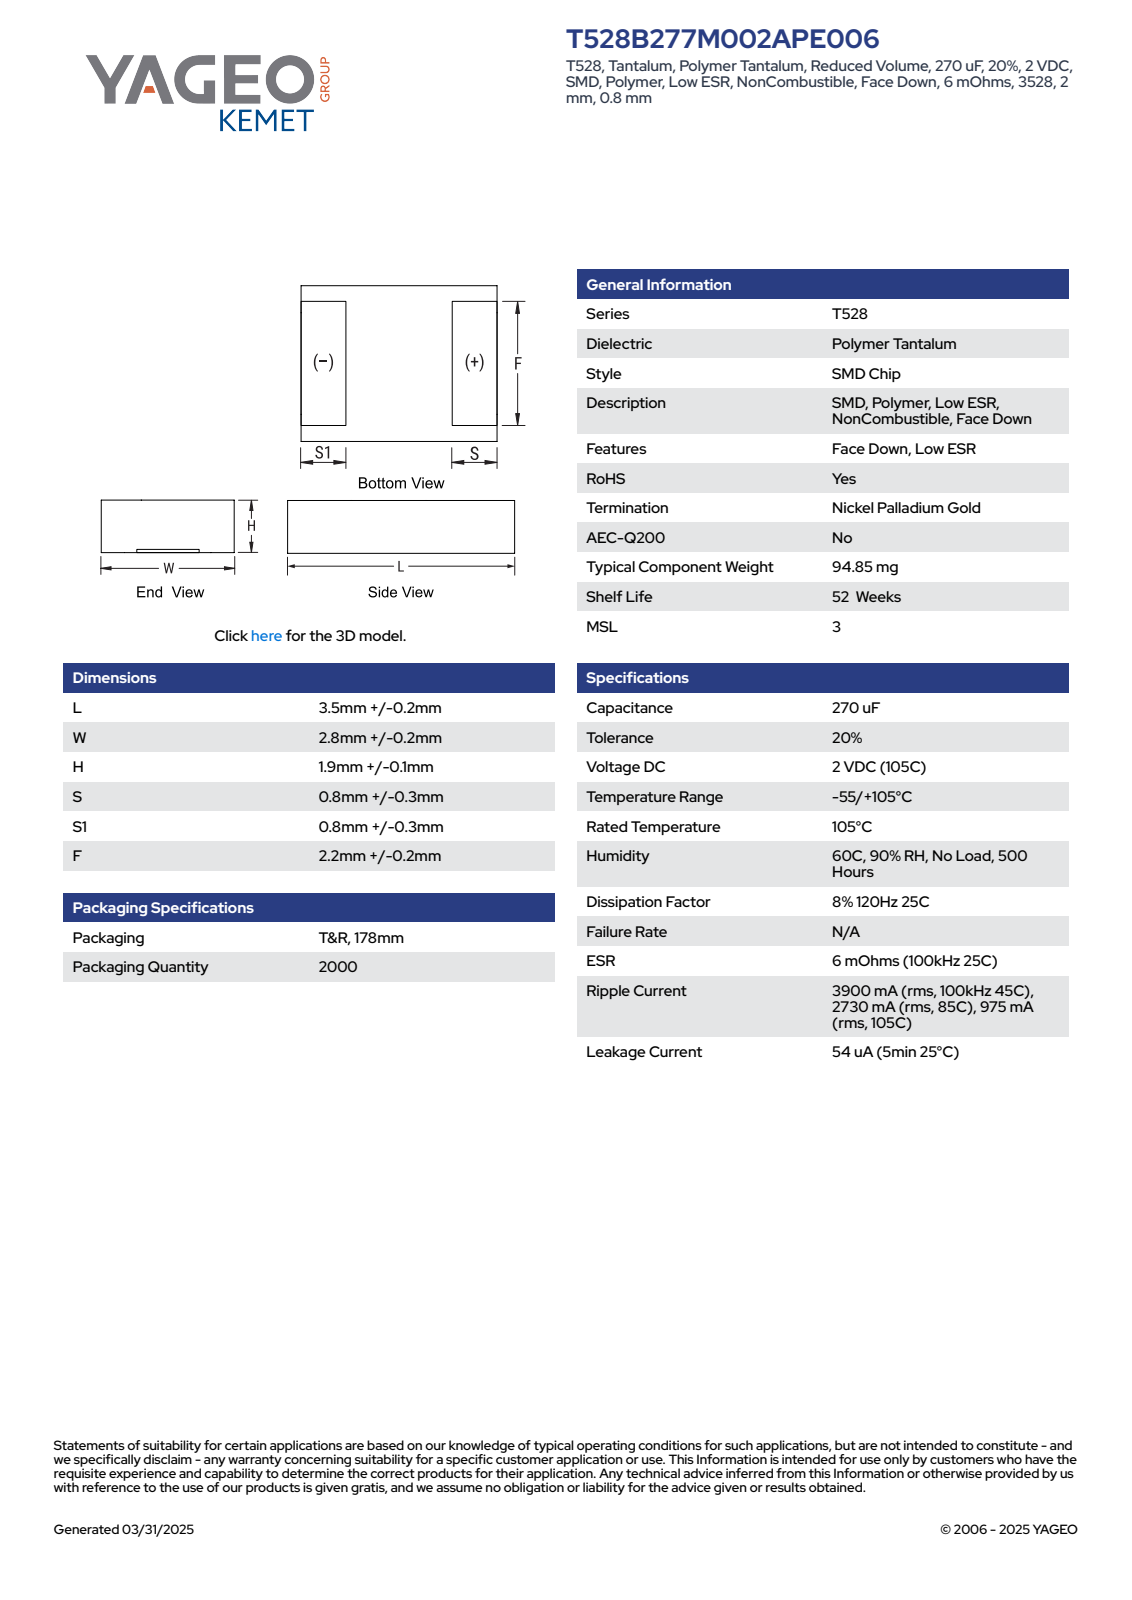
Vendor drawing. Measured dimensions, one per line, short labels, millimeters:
name: CTS_528B_L3.7W3H2S0.8F2.4
written by: SolidWorks 2014 (AUTOMOTIVE_DESIGN)
unit: mm
bodies: 4 solids, 75 faces (75 planar, 0 cylindrical, 0 other)
size: 3.71 × 3 × 2.01
volume: 22 mm³; area: 51 mm²
face distances: 3, 2, 3.7, 2.01, 3.71, 3.72, 0.8, 0.81, 2.91, 2.9
